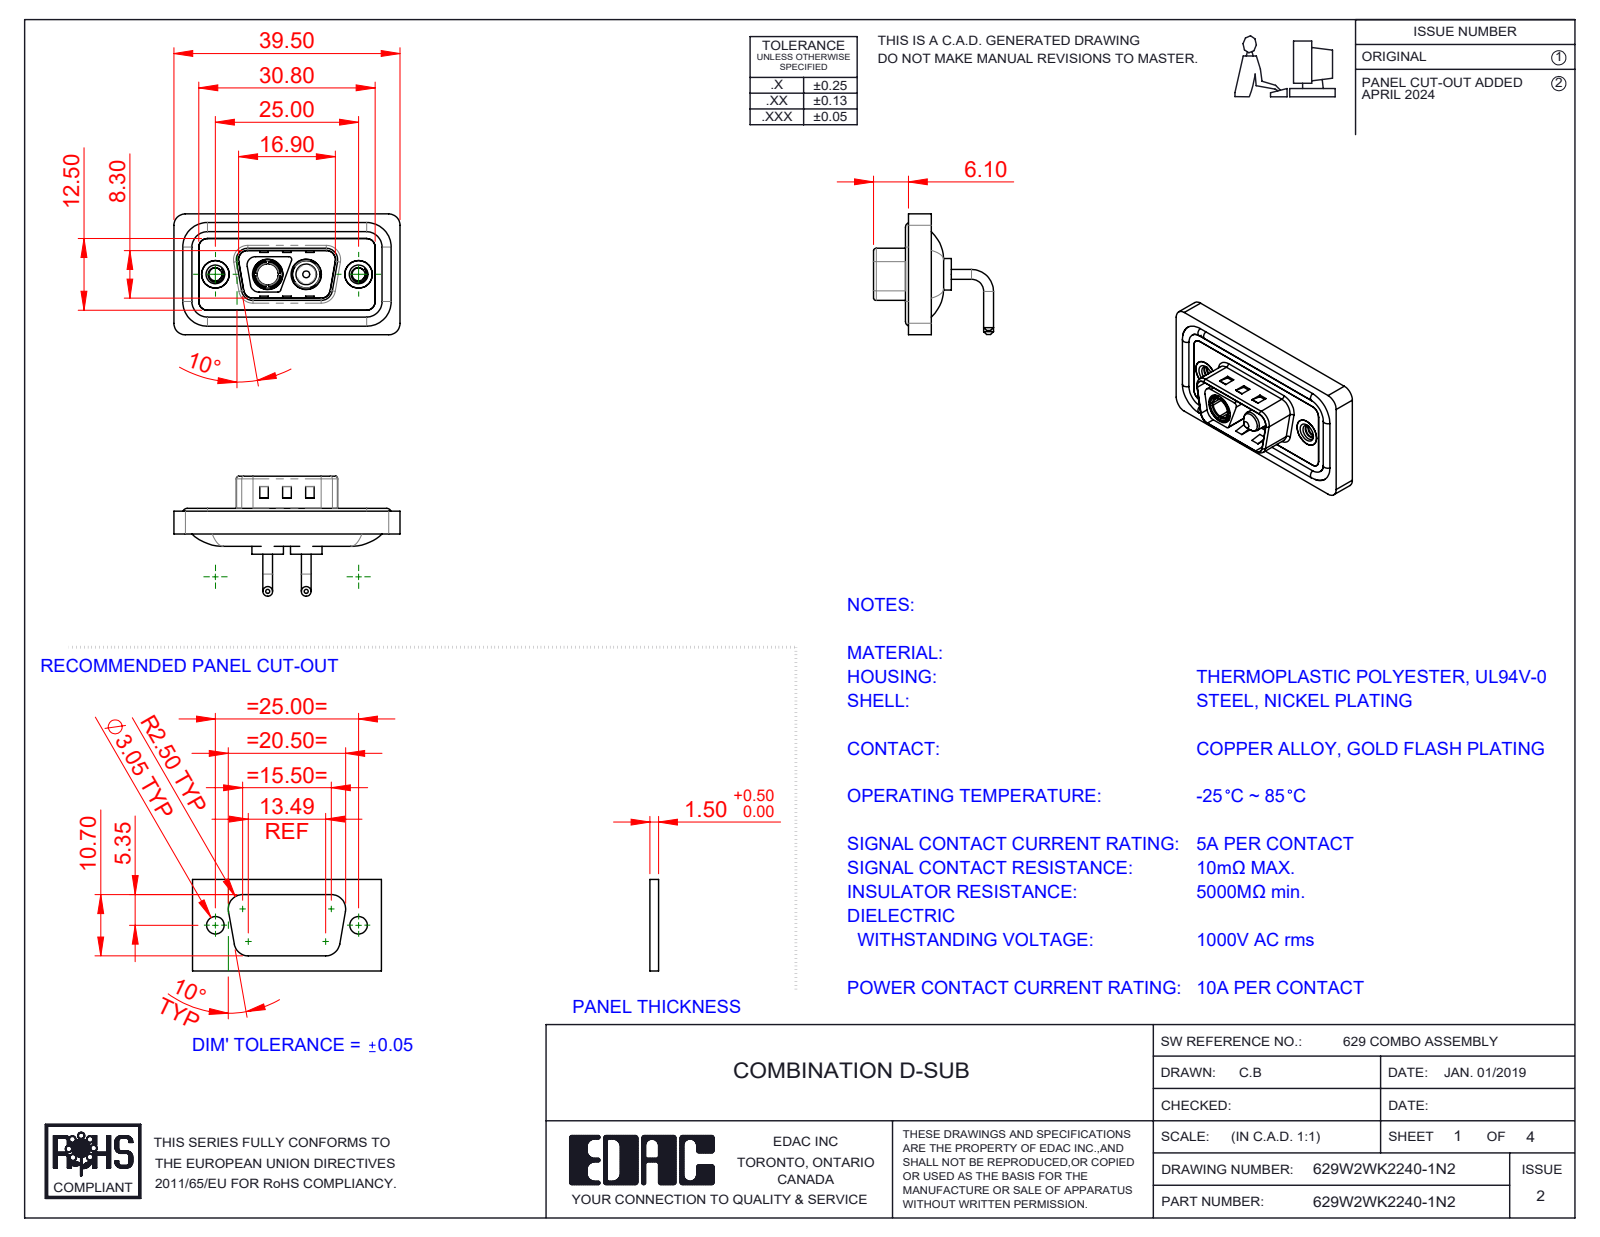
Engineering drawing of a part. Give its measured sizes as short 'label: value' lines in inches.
name: Power Pin_10A RA; 629W2WK2140-1N2; Power Socket_10A RA; 629Combo Threaded Rivet_2 (+4 more)
written by: SolidWorks 2023 (CONFIG_CONTROL_DESIGN)
unit: in
bodies: 11 solids, 542 faces (189 planar, 231 cylindrical, 122 other)
size: 1.555 × 0.831 × 0.825
volume: 0.279 in³; area: 11.51 in²
holes: 2× ⌀0.089, 2× ⌀0.157, 2× ⌀0.189, 2× ⌀0.191, 2× ⌀0.197, 2× ⌀0.209, 1× ⌀0.146
bosses: 4× ⌀0.067, 4× ⌀0.063, 2× ⌀0.217, 2× ⌀0.205, 2× ⌀0.193, 2× ⌀0.187, 2× ⌀0.148, 1× ⌀0.195
rounds: 20× R0.059, 18× R0.079, 10× R0.02, 8× R0.063, 4× R0.01, 4× R0.024, 4× R0.026, 4× R0.035
face distances: 0.016, 0.114, 0.043, 0.031, 0.083, 0.098, 0.122, 0.063, 0.177, 0.059
hole spacings: 0.36, 0.624, 0.265, 0.984
